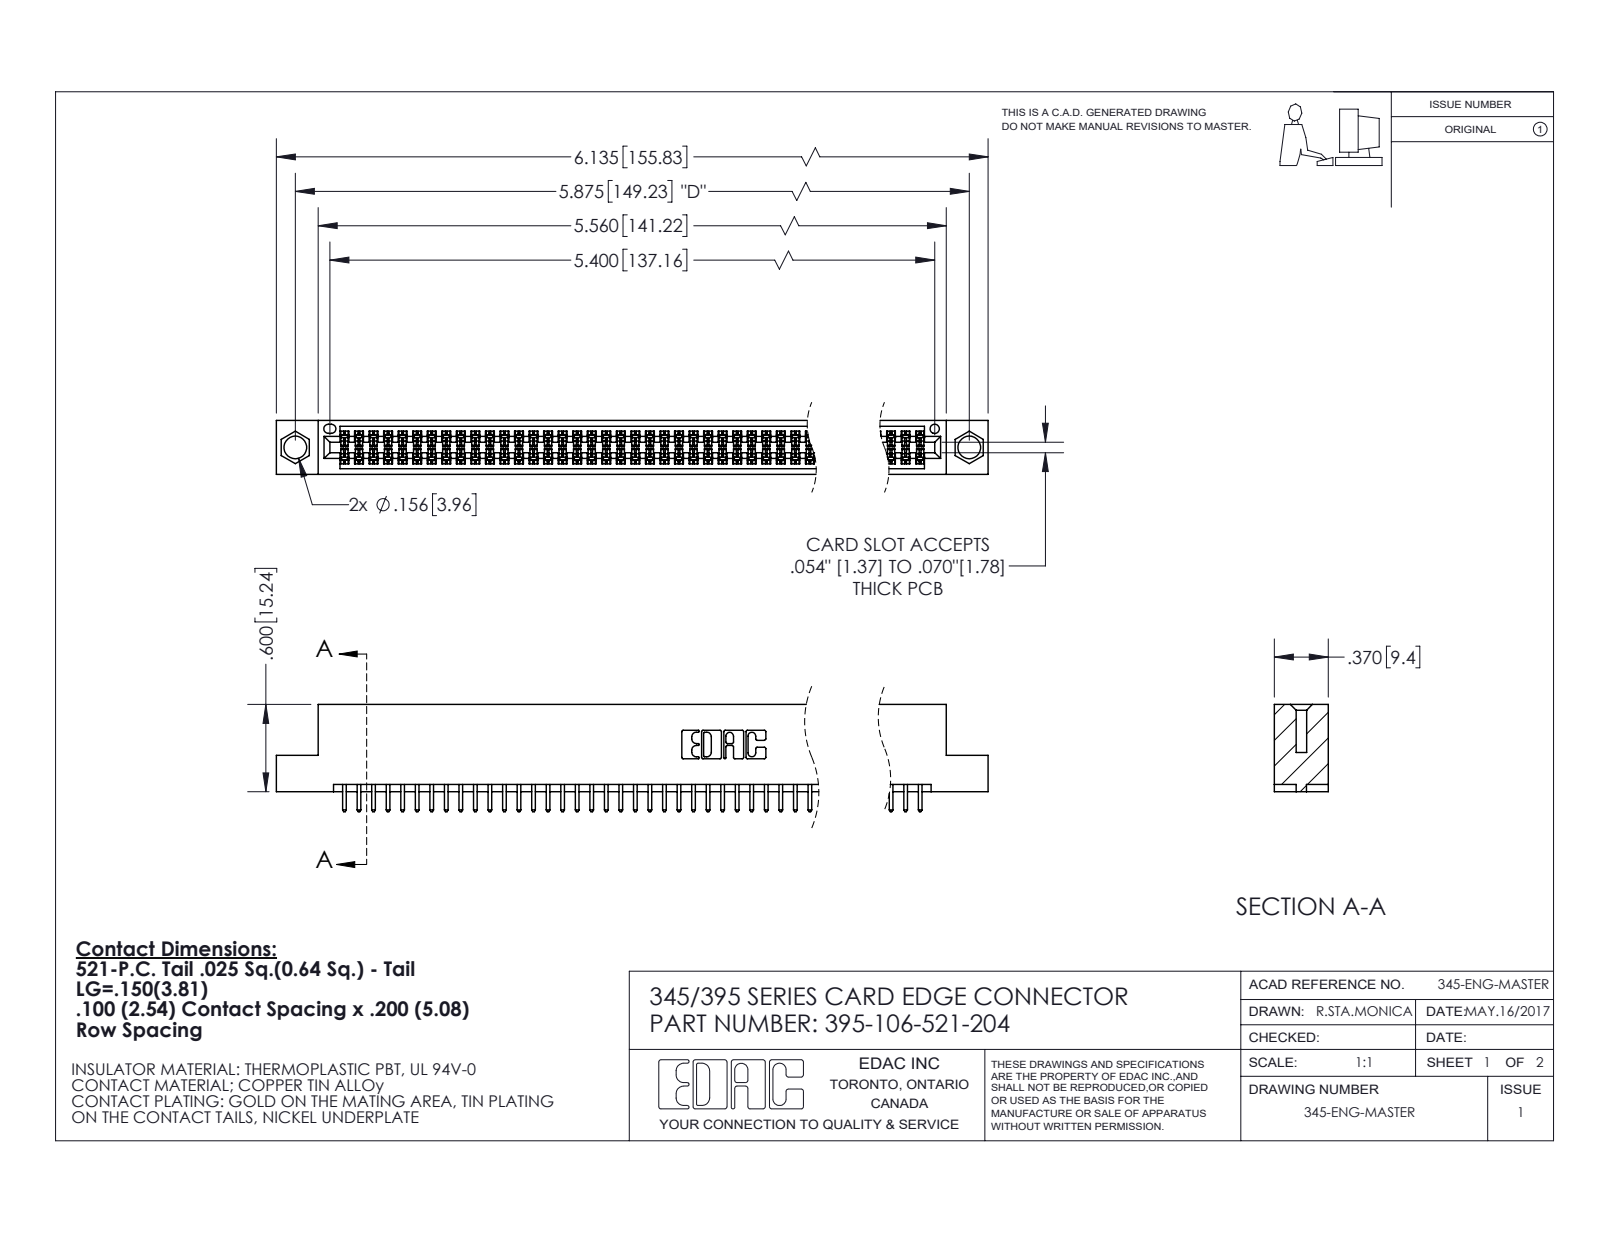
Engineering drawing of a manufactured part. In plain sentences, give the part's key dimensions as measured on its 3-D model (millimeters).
The part is named "345 Part_Flush Mounting Lugs - 0.156 Dia-TI; 345-292-001_345-293-121; 395-106-521-204". Its 3-D file was written by "SolidWorks 2020 (CONFIG_CONTROL_DESIGN)". It is 107 solids with 5440 faces: 3592 planar, 1848 cylindrical and 0 other. Overall it measures 155.8 by 18.7 by 9.4 millimeters. Its volume is 15 100 cubic millimeters and its surface area 22 090 square millimeters. Round holes: 2 of diameter 4, 1 of diameter 1.6. Partial cylindrical surfaces (rounded edges, fillets, slot ends): 159 of radius 0.2, 106 of radius 0.3, 22 of radius 0.3, 6 of radius 0.2, 6 of radius 0.8, 3 of radius 0.7, 2 of radius 0.4, 2 of radius 0.5. The main face-to-face distances are 7.6, 1.8, 5.1, 9.4, 2.5, 6.9, 0.6, 5.7, 4.4, 3.8. The hole center spacings are 6.9, 143.2, 149.2.
